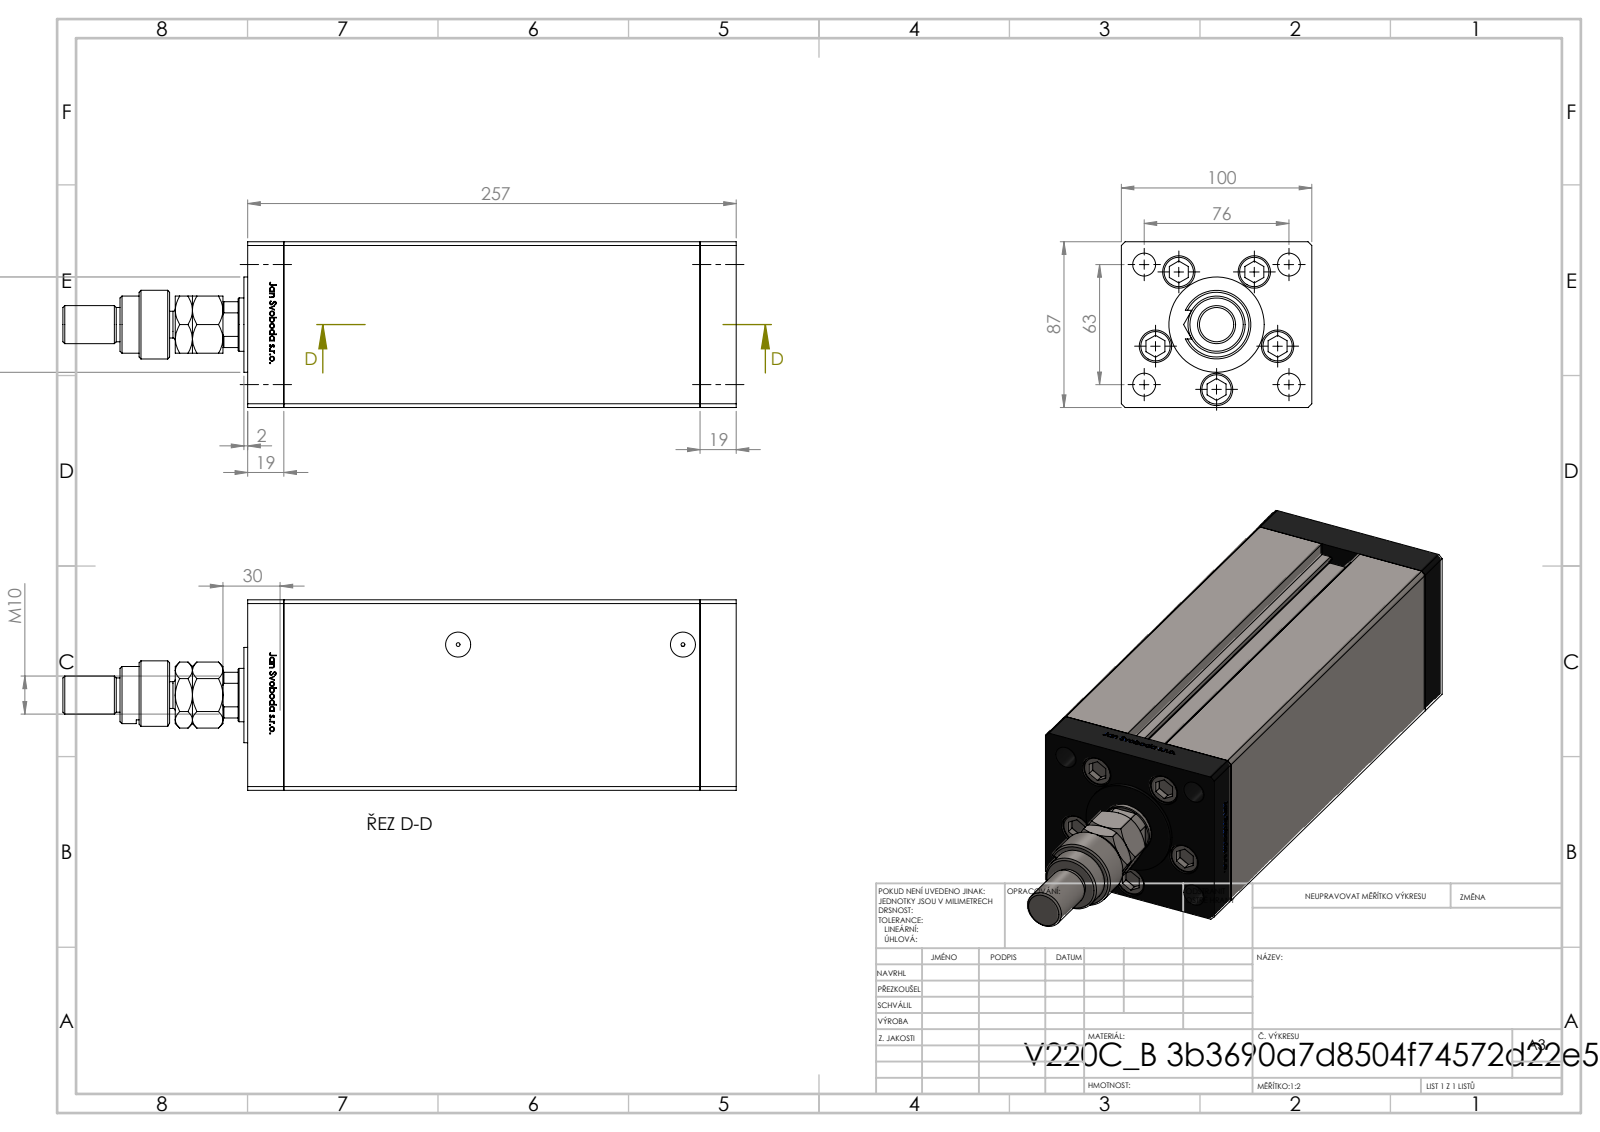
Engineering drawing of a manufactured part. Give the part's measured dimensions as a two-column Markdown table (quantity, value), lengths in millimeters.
| quantity | value |
| --- | --- |
| part name | ALLEN BOLT; V220C_VC_B; MFA; V220C BACK_B (+3 more) |
| STEP written by | SolidWorks 2019 (CONFIG_CONTROL_DESIGN) |
| units | millimeters |
| bodies | 16 solids, 1270 faces (492 planar, 160 cylindrical, 618 other) |
| overall size | 353.5 × 100 × 87 |
| volume | 1 982 000 mm³ |
| surface area | 263 290 mm² |
| round holes (diameter × count) | 13.5 × 7, 17 × 5, 12 × 4, 2 × 2, 13.16 × 2, 18.5 × 1, 28 × 1 |
| round bosses / shafts (diameter × count) | 8 × 5, 17 × 2, 50 × 1, 36 × 1, 30 × 1, 22 × 1, 20 × 1, 18 × 1 |
| partial cylindrical surfaces (radius × count) | 0.93 × 2, 7.5 × 1, 12 × 1, 13.5 × 1 |
| main face-to-face distances | 100, 87, 19, 218.5, 237.5, 34.25, 256.5, 15.25, 203.25, 222.25 |
| hole center spacings | 34, 18.59, 39.64, 49.36, 57.95, 21.03, 38.08, 39.27 |
